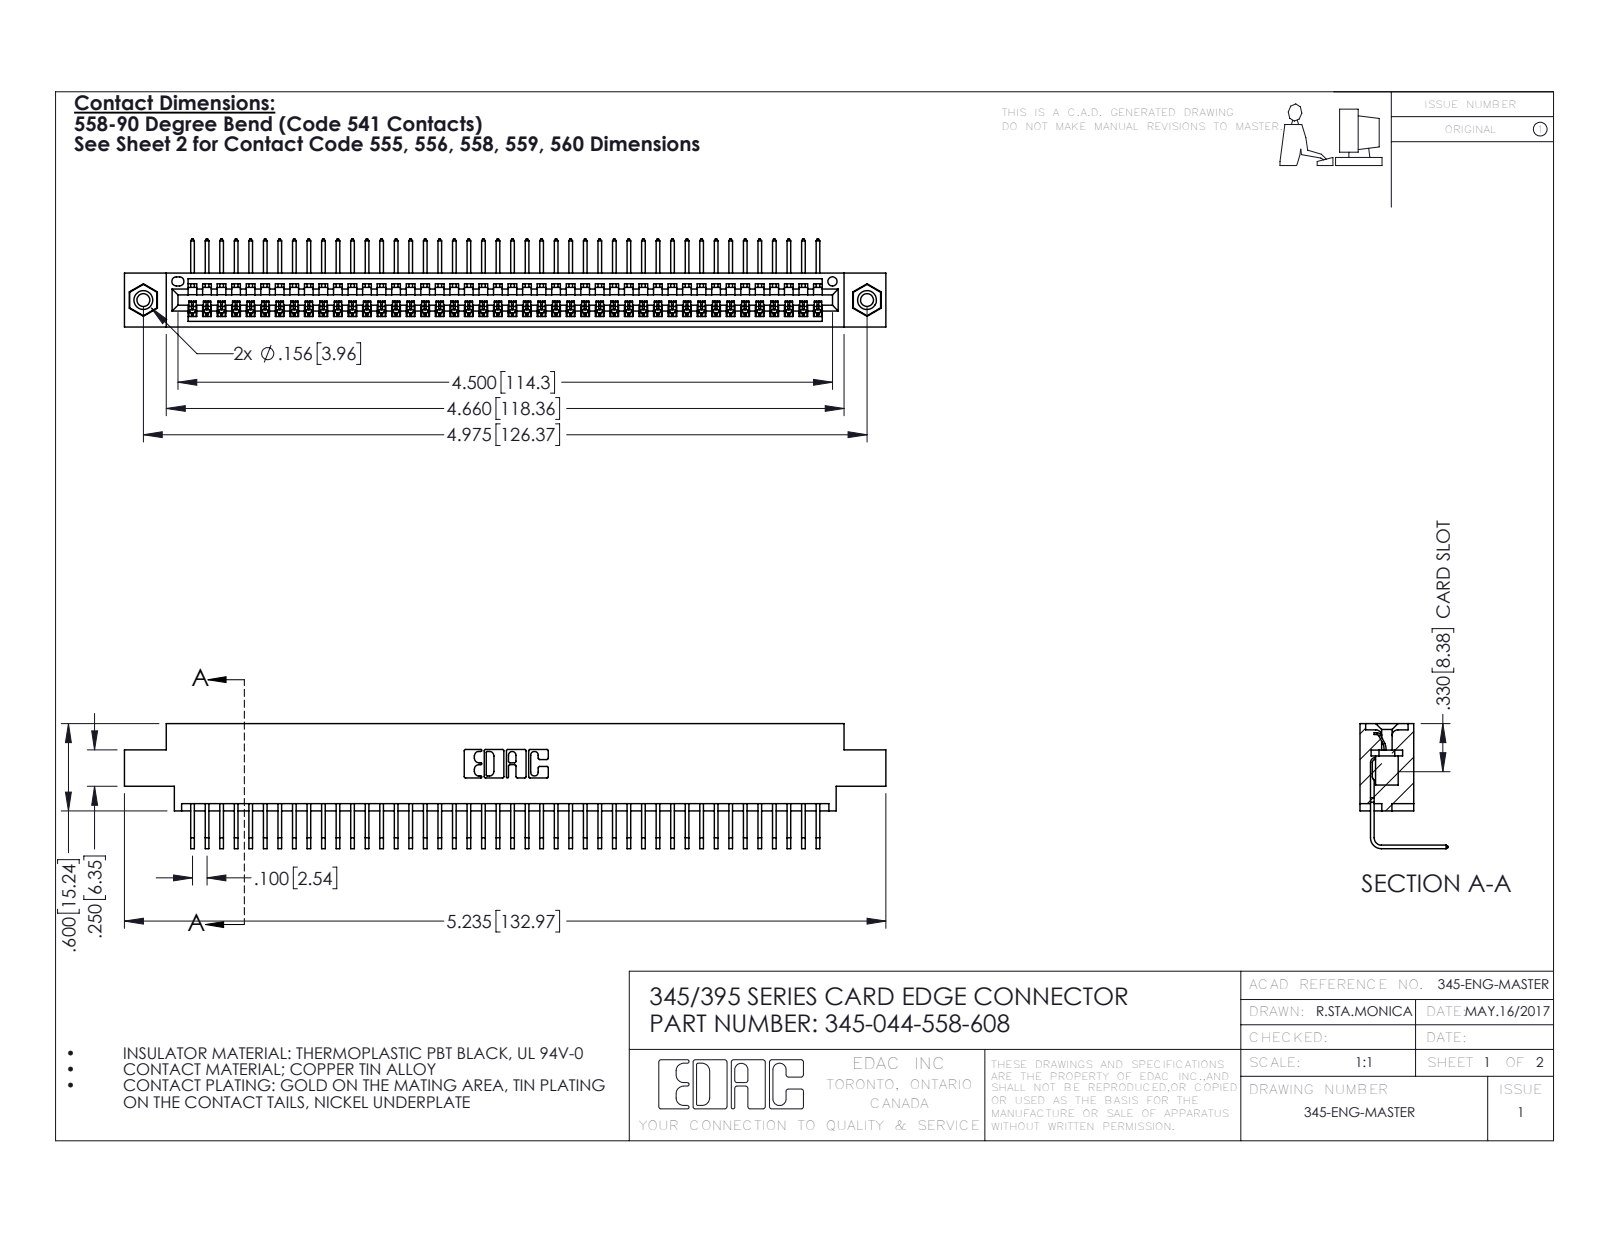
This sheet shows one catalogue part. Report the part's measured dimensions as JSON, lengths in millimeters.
{"part_name": "345 Part_0.170 Offset - 0.156 Dia-TI; 345-044-558-608; 345-250-001_345-250-003-102; 345-292-001_558 Tail - 2", "step_written_by": "SolidWorks 2016 (CONFIG_CONTROL_DESIGN)", "units": "millimeters", "bodies": {"solids": 47, "faces": 2830, "planar": 1964, "cylindrical": 850, "other": 16}, "overall_size": [133, 21.8, 15.4], "volume_mm3": 12700, "surface_area_mm2": 17880, "round_holes": [[2.3, 2], [3.2, 2], [4, 2], [1.6, 1]], "round_bosses_or_shafts": [[3.9, 2]], "partial_cylinders_radius": [[0.2, 88], [0.3, 22], [0.2, 6], [0.8, 6], [0.7, 3], [0.8, 2], [1, 2], [0.4, 1]], "face_to_face_distances": [1.8, 7.6, 9.4, 5.1, 2.5, 6.9, 0.6, 5.7, 4.4, 3.8], "hole_center_spacings": [6.9, 120.4, 126.4]}
